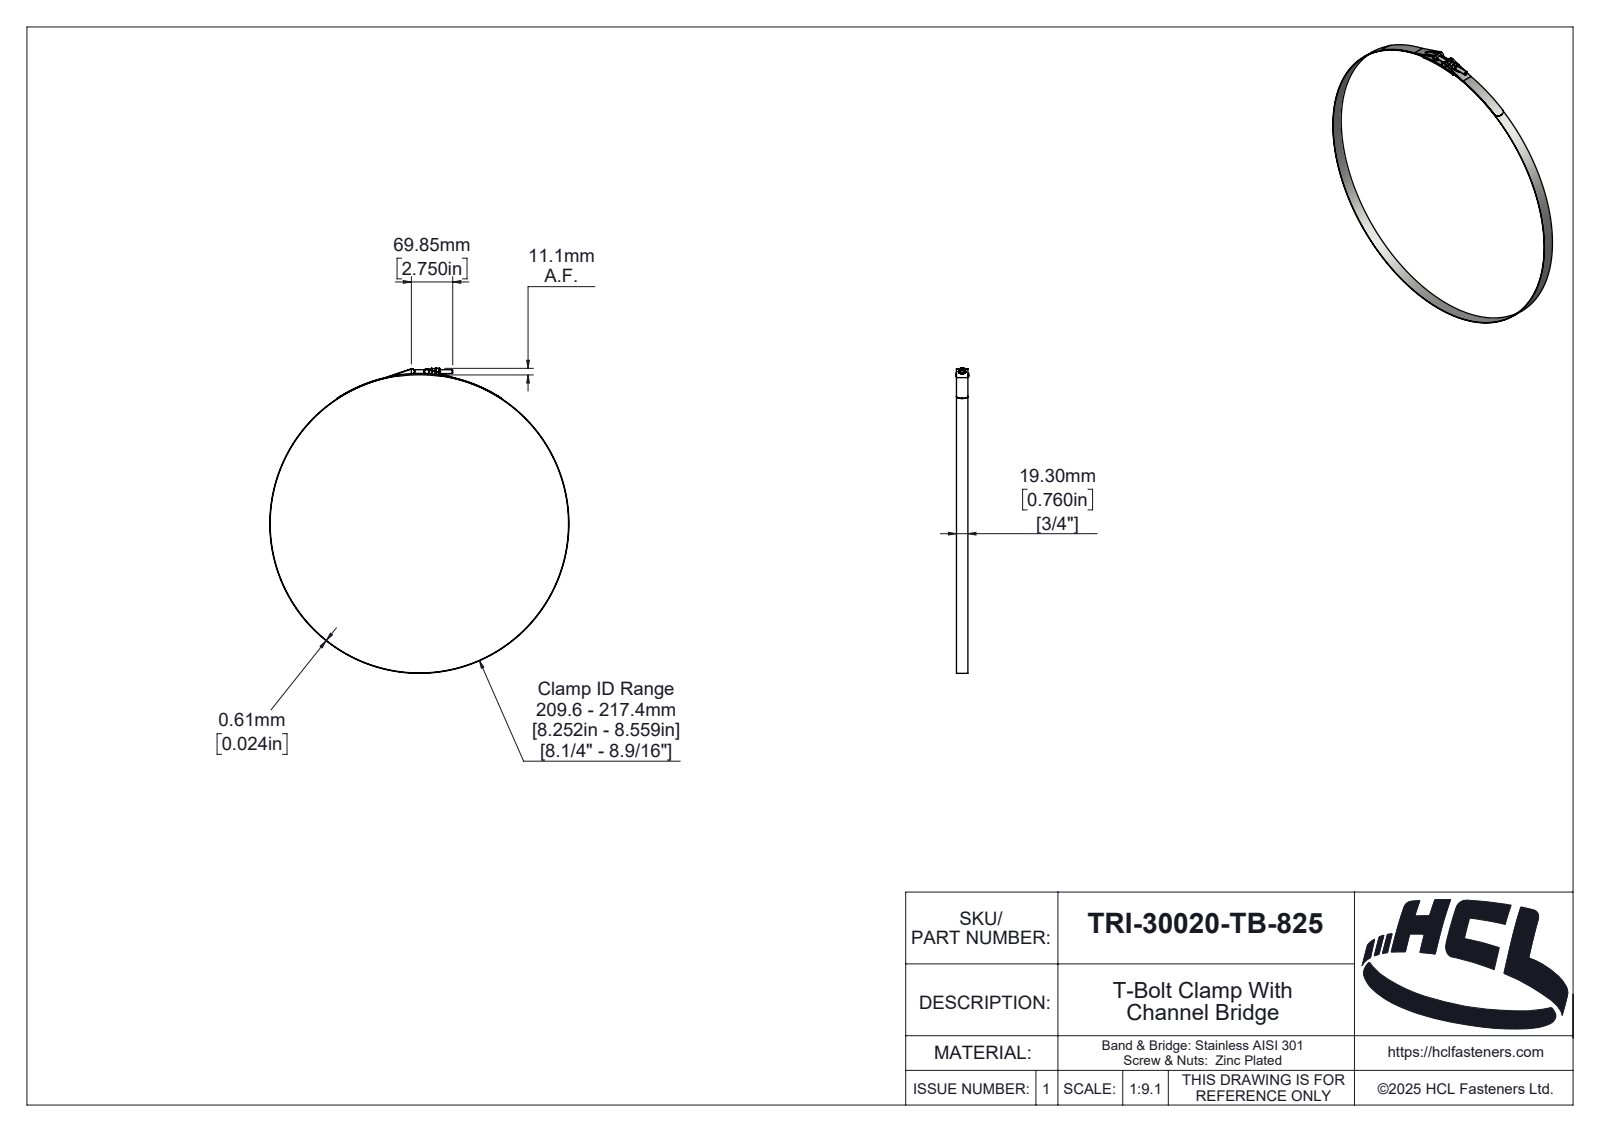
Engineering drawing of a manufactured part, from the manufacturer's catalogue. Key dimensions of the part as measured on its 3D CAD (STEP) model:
Part name (STEP PRODUCT): TRI-30020-TB-825
STEP written by: SolidWorks 2025 (AUTOMOTIVE_DESIGN)
Units: millimetres
Bodies: 6 solids, 330 faces (44 planar, 122 cylindrical, 164 other)
Overall size (bounding box): 515.03 × 505.22 × 22
Volume: 26 694 mm³ · Surface area: 80 670 mm²
Round holes (diameter × count): ⌀5.4 ×1, ⌀6.35 ×1, ⌀6.5 ×1, ⌀7.58 ×1, ⌀504 ×1
Round bosses / shafts (diameter × count): ⌀8.58 ×2, ⌀505.22 ×1, ⌀10.58 ×1
Partial cylindrical surfaces — rounded edges, fillets, slot ends (radius × count): R0.39 ×6, R0.5 ×2, R4.39 ×2, R5 ×2, R0.59 ×1, R2.42 ×1, R3.03 ×1, R3.19 ×1
Main face-to-face distances: 0.61, 19.3, 1.35, 20.65, 0.74, 21.39, 20.04, 22, 20.78, 11.11
Hole centre spacings: 257
